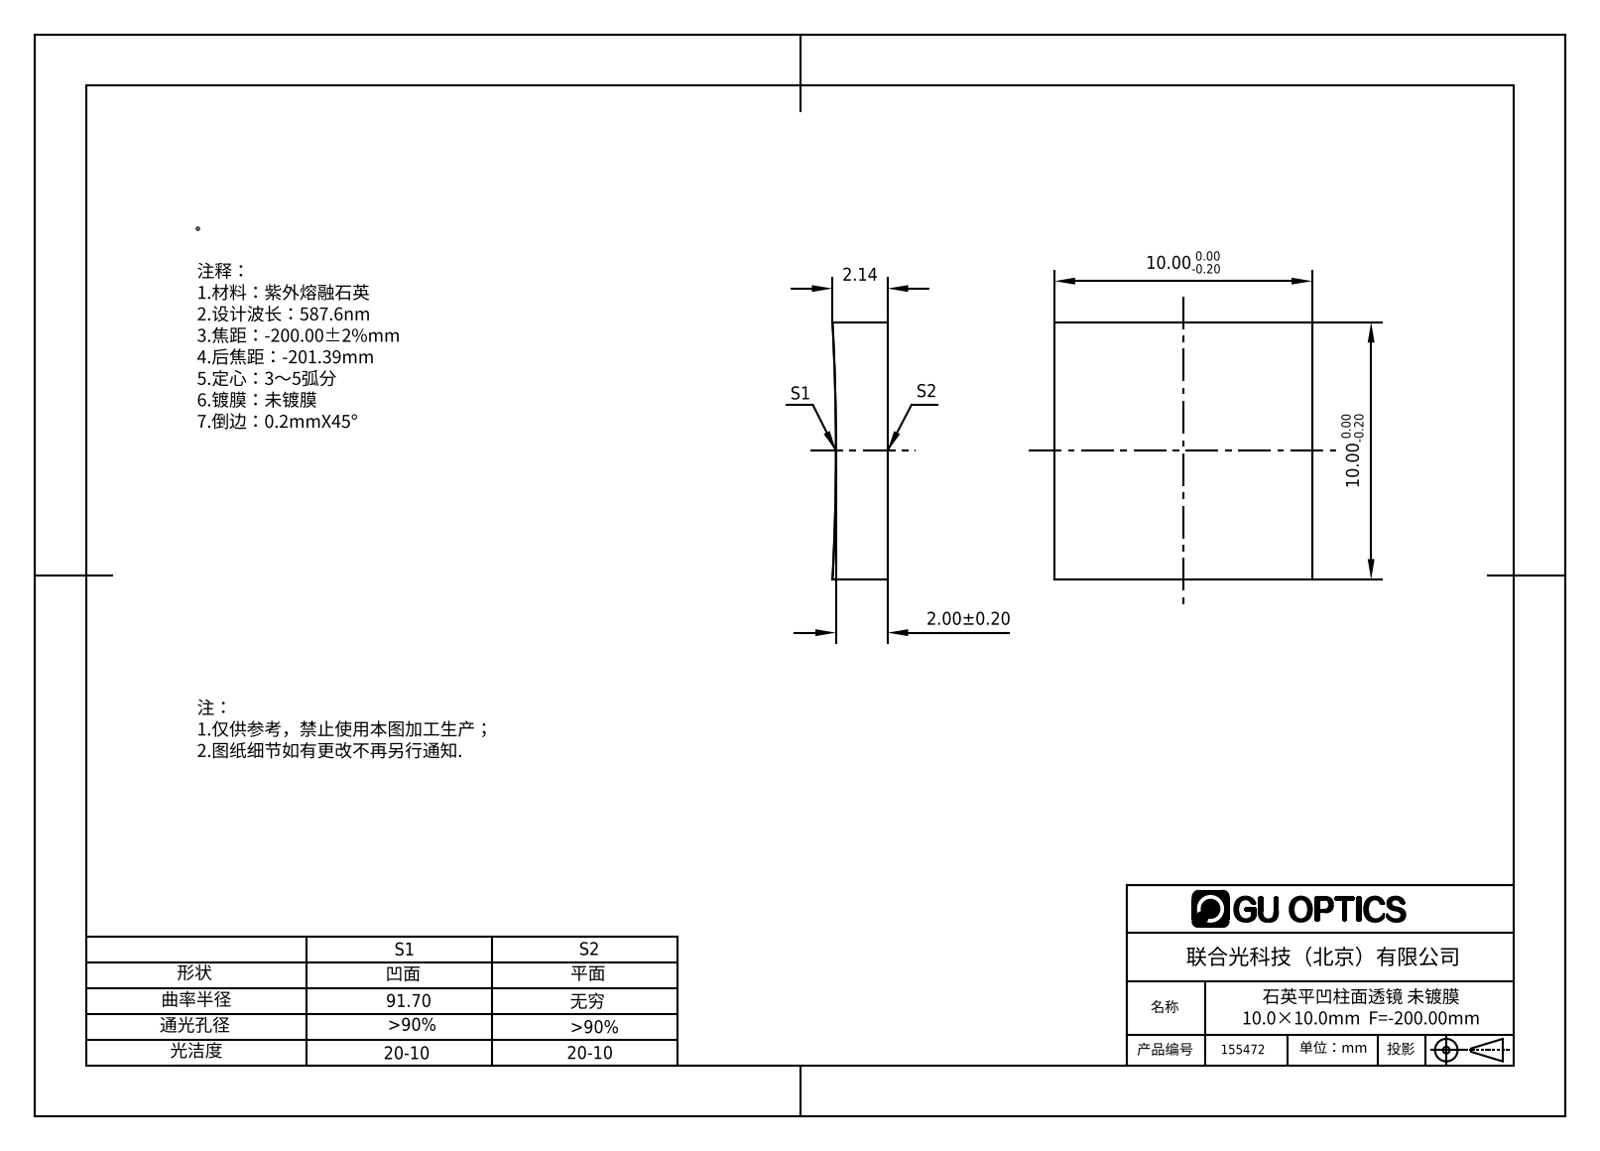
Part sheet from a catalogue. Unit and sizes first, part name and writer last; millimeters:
Units: millimetres
Overall size (bounding box): 10 × 10 × 2.14
Partial cylindrical surfaces — rounded edges, fillets, slot ends (radius × count): R91.7 ×1
Main face-to-face distances: 10
Volume: 205 mm³ · Surface area: 284 mm²
Bodies: 1 solid, 6 faces (5 planar, 1 cylindrical, 0 other)
Part name (STEP PRODUCT): 155472
STEP written by: SolidWorks 2016 (AUTOMOTIVE_DESIGN)
